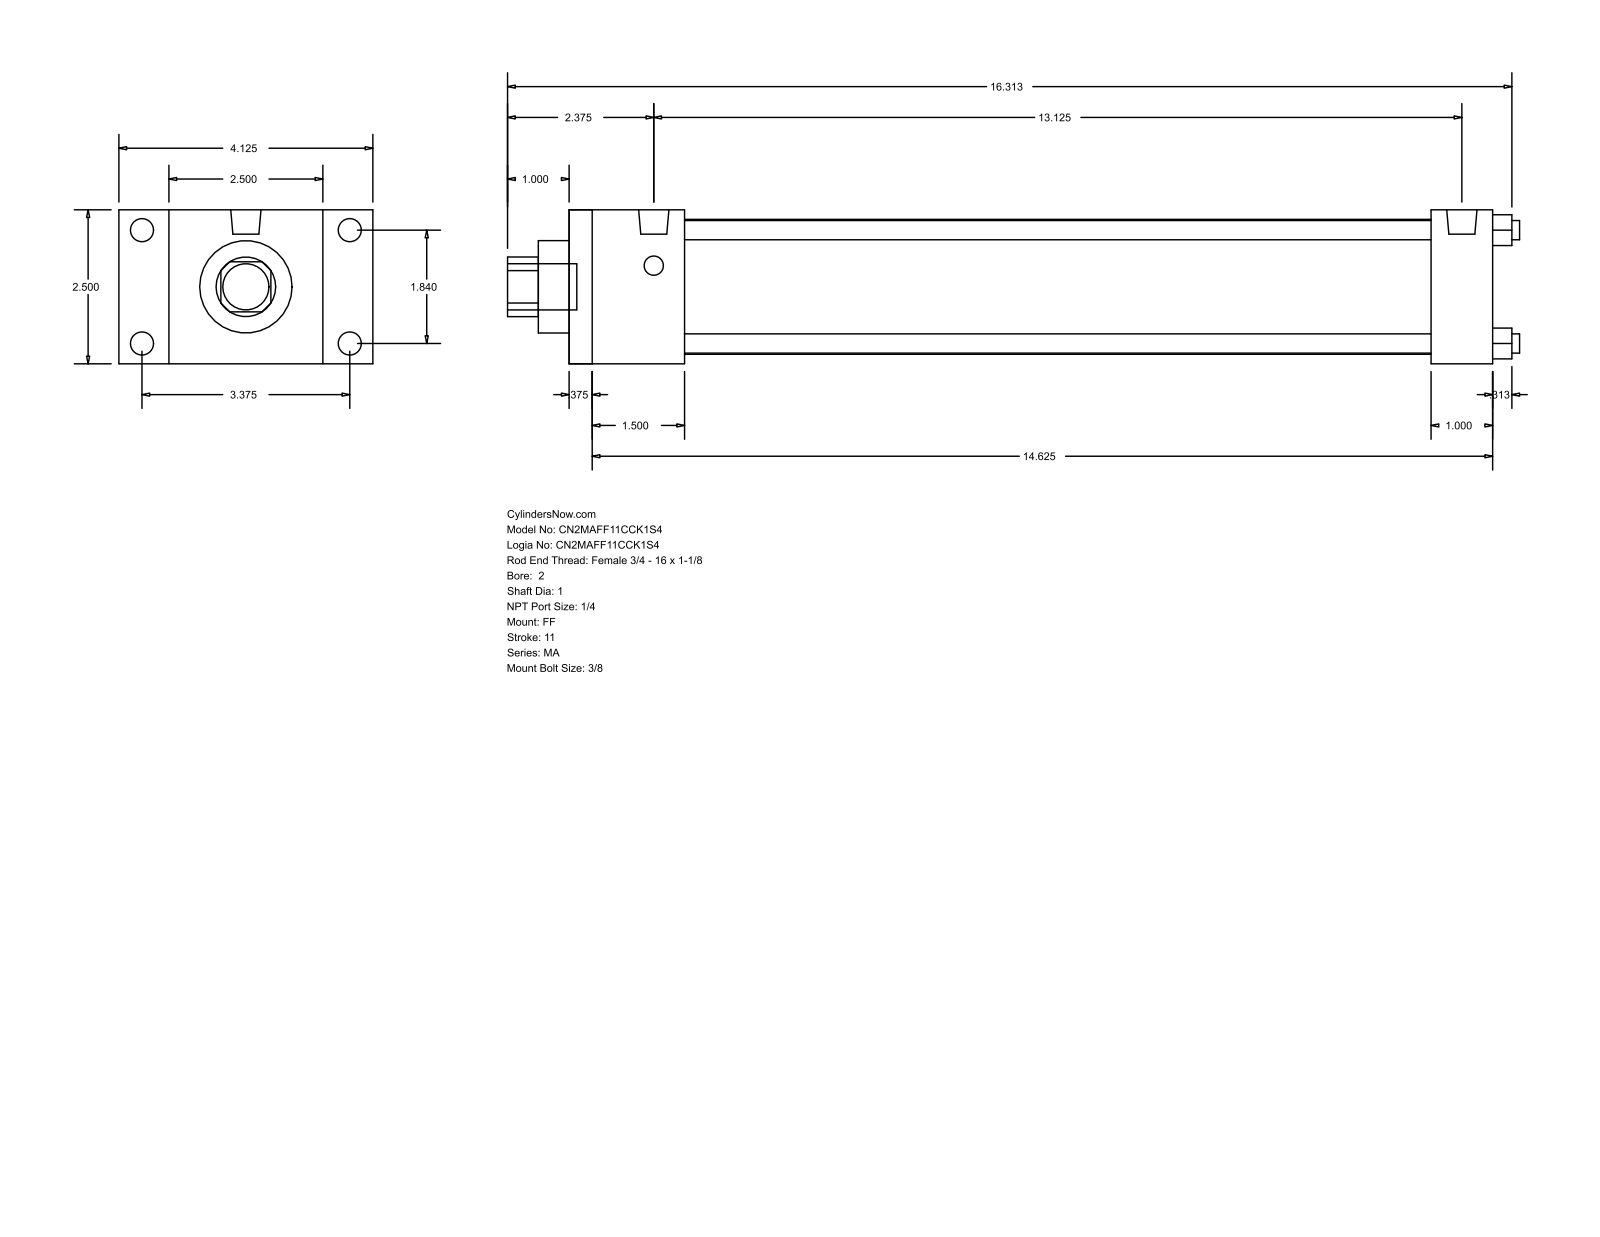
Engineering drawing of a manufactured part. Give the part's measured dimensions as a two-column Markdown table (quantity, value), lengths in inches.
| quantity | value |
| --- | --- |
| part name | MA_FF__0200_1 |
| STEP written by | GSSL Pune (CONFIG_CONTROL_DESIGN) |
| units | inches |
| bodies | 0 solids, 92 faces (64 planar, 28 cylindrical, 0 other) |
| overall size | 16.437 × 4.125 × 2.5 |
| round holes (diameter × count) | 0.313 × 4, 1 × 1, 1.5 × 1, 2.19 × 1 |
| round bosses / shafts (diameter × count) | 0.375 × 4, 0.313 × 4, 0.492 × 2, 0.75 × 1 |
| partial cylindrical surfaces (radius × count) | 0.484 × 1 |
| main face-to-face distances | 2.5, 15, 0.375, 14.625, 1, 0.813, 0.5, 1.875, 14, 1.5 |
| hole center spacings | 1.301, 1.84, 2.602 |
